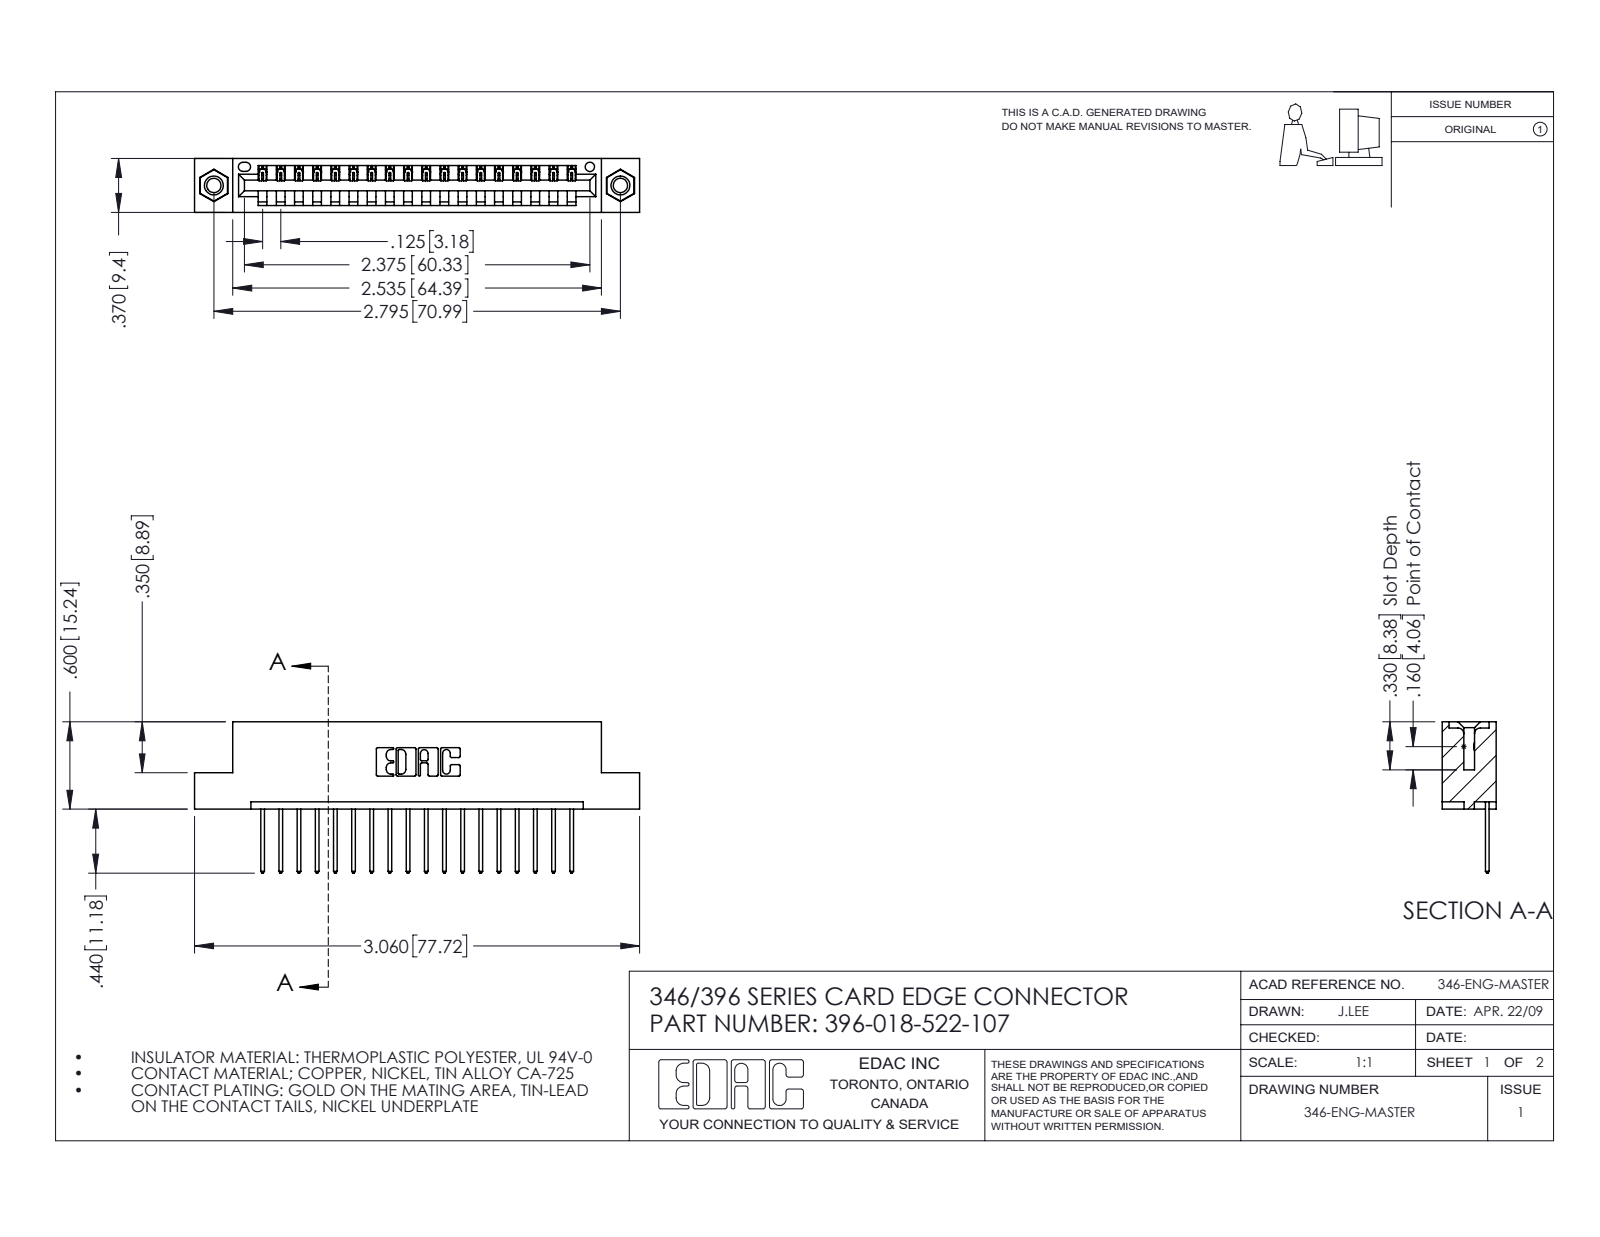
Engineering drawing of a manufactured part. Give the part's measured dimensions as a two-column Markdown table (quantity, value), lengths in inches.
| quantity | value |
| --- | --- |
| part name | 345-292-001_345-293-122; 346 Part_Flush Mounting Lugs - 0.156 Dia-TI; 345-250-001_345-250-005-103; 396-018-522-107 |
| STEP written by | SolidWorks 2016 (CONFIG_CONTROL_DESIGN) |
| units | inches |
| bodies | 21 solids, 1226 faces (828 planar, 382 cylindrical, 16 other) |
| overall size | 3.06 × 1.04 × 0.37 |
| volume | 0.443 in³ |
| surface area | 13.83 in² |
| round holes (diameter × count) | 0.098 × 2, 0.125 × 2, 0.156 × 2, 0.064 × 1 |
| round bosses / shafts (diameter × count) | 0.155 × 2 |
| partial cylindrical surfaces (radius × count) | 0.006 × 36, 0.01 × 36, 0.01 × 22, 0.007 × 6, 0.031 × 6, 0.026 × 3, 0.031 × 2, 0.04 × 2 |
| main face-to-face distances | 0.048, 0.322, 0.25, 0.37, 0.072, 0.298, 0.025, 0.148, 0.222, 0.1 |
| hole center spacings | 0.246, 2.588, 2.795 |
